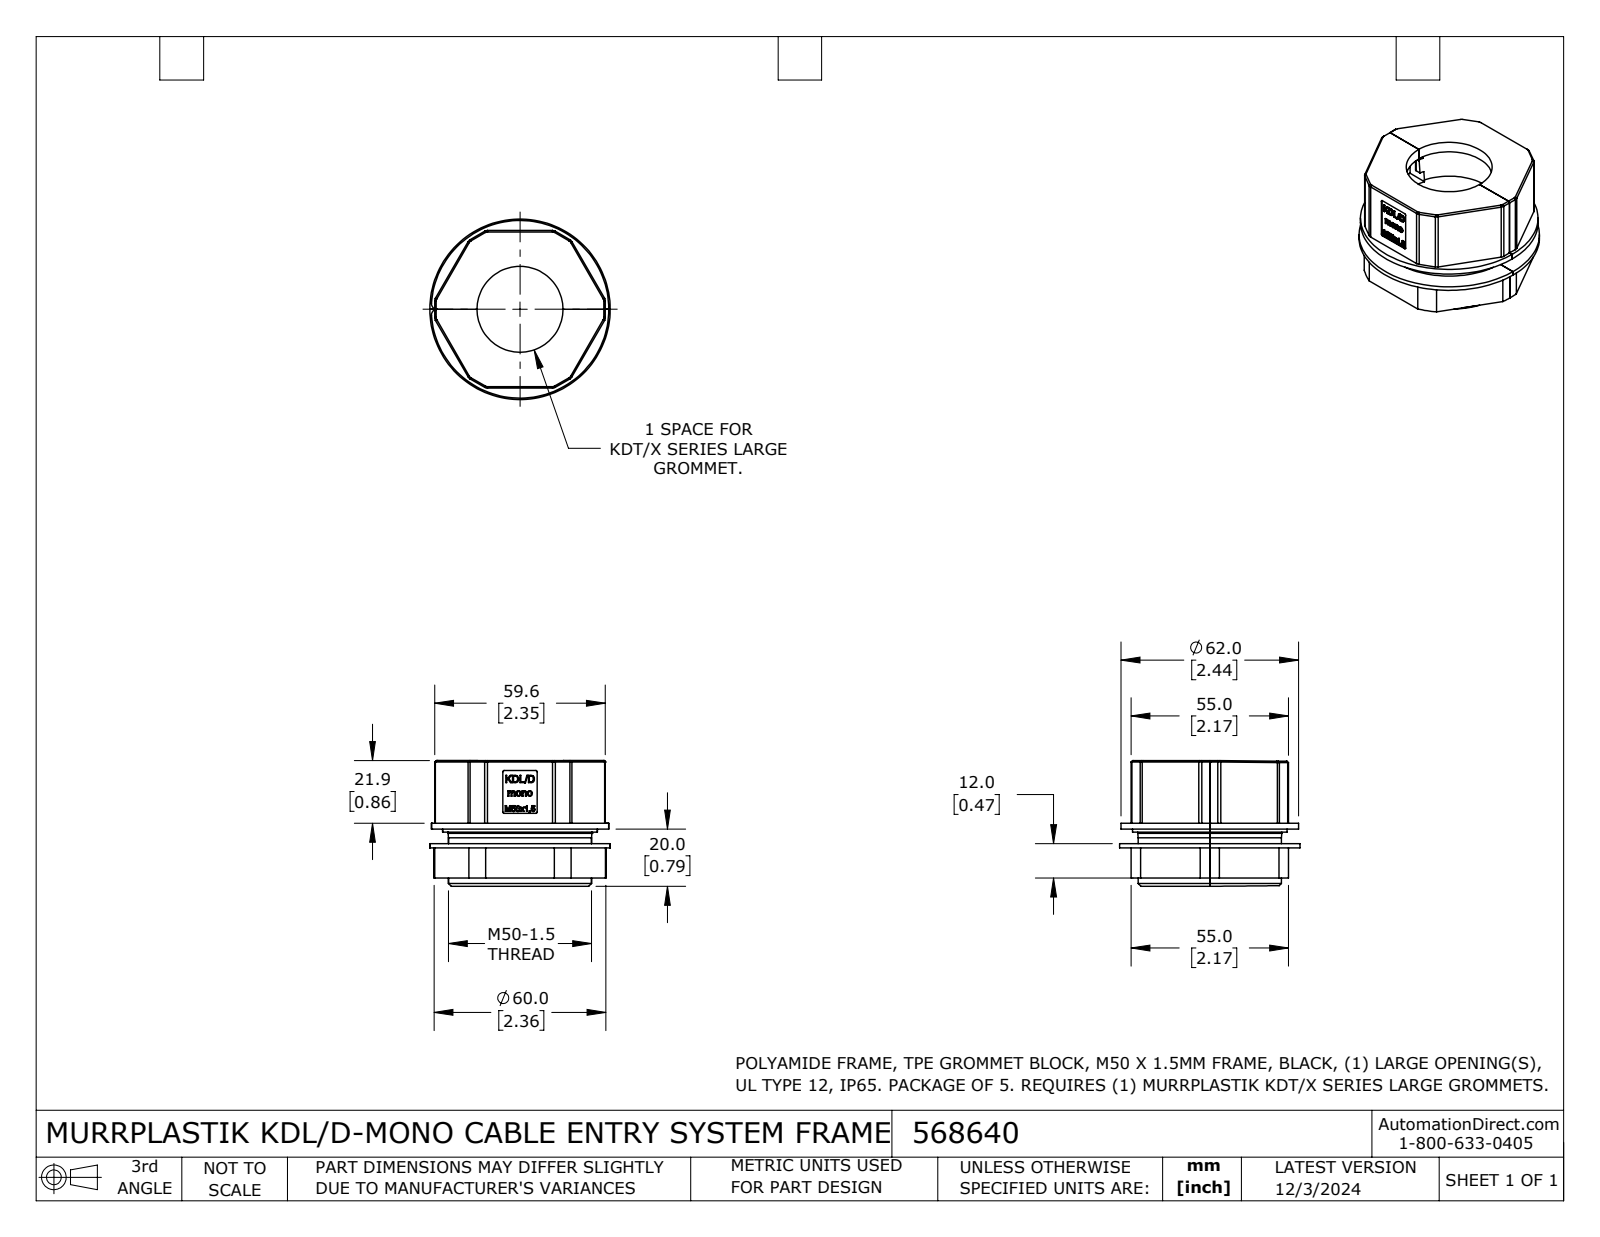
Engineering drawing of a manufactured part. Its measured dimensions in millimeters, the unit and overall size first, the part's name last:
Units: millimetres
Overall size (bounding box): 63 × 63 × 43.9
Round holes (diameter × count): ⌀30 ×1, ⌀35 ×1, ⌀42 ×1, ⌀50 ×1, ⌀50 ×1
Round bosses / shafts (diameter × count): ⌀63 ×1, ⌀62 ×1, ⌀54 ×1, ⌀50.2 ×1
Partial cylindrical surfaces — rounded edges, fillets, slot ends (radius × count): R2 ×14, R0.5 ×8, R0.3 ×4, R0.4 ×4, R0.6 ×4, R1 ×1, R30 ×1
Main face-to-face distances: 55, 5.1, 27.5, 23.9, 29, 12, 41, 17.1, 6.6, 30.5
Volume: 58 980 mm³ · Surface area: 26 810 mm²
Bodies: 6 solids, 497 faces (273 planar, 81 cylindrical, 143 other)
Part name (STEP PRODUCT): 568640
STEP written by: SolidWorks 2023 (CONFIG_CONTROL_DESIGN)
